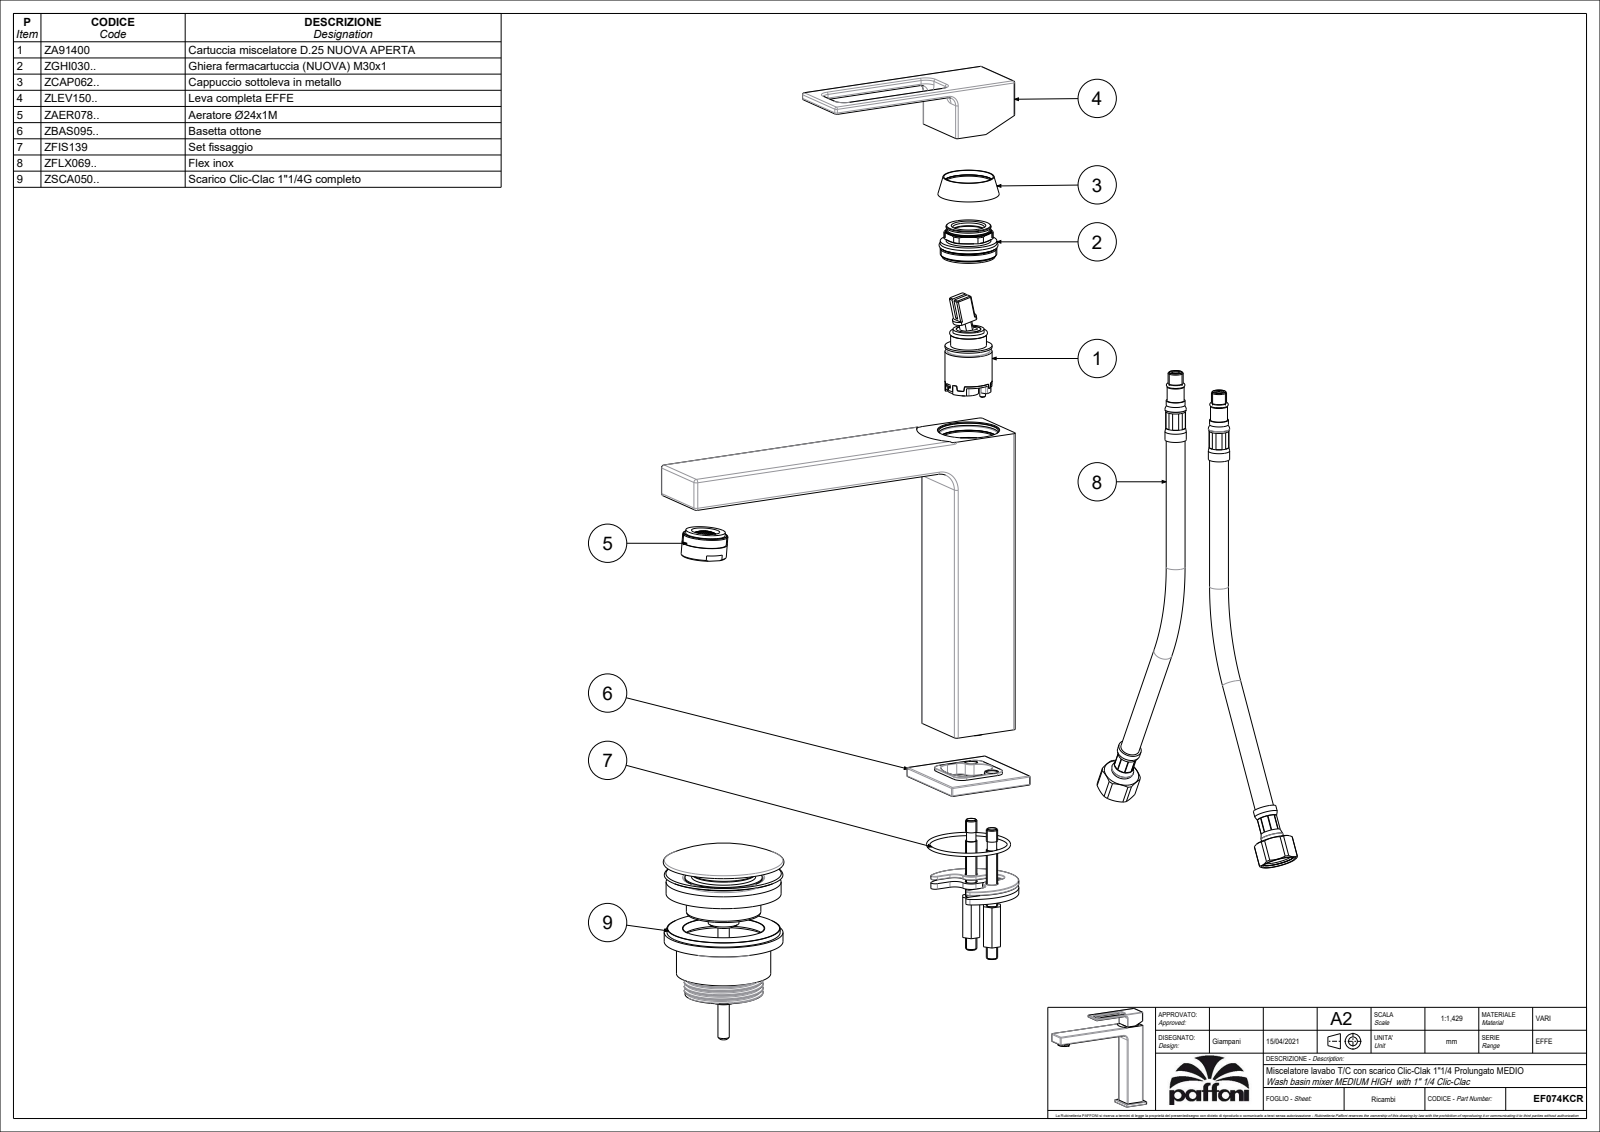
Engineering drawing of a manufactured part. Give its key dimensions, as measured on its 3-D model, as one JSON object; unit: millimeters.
{"part_name": "EF074CR", "step_written_by": "CREO PARAMETRIC BY PTC INC, 2020044 (CONFIG_CONTROL_DESIGN)", "units": "millimeters", "bodies": {"solids": 6, "faces": 1963, "planar": 1553, "cylindrical": 236, "other": 174}, "overall_size": [202, 196.28, 48], "volume_mm3": 174231, "surface_area_mm2": 99723, "round_holes": [[5.5, 3], [6, 2], [6.2, 2], [7, 2], [8.2, 2], [9, 2], [3, 1], [4.2, 1], [4.5, 1], [7.8, 1], [16, 1], [17, 1]], "round_bosses_or_shafts": [[11, 2], [41.8, 1], [24, 1], [19.5, 1], [18.8, 1], [16.8, 1], [7.6, 1]], "partial_cylinders_radius": [[1, 66], [1.5, 20], [0.5, 14], [5, 9], [0.25, 6], [4, 6], [3.5, 2], [4.7, 2]], "face_to_face_distances": [3.5, 33.5, 37, 30, 13.5, 17, 0.5, 3, 10, 41.78], "hole_center_spacings": [8.14, 11, 11.4, 13.6, 15.04, 17.87, 21.64, 22]}
